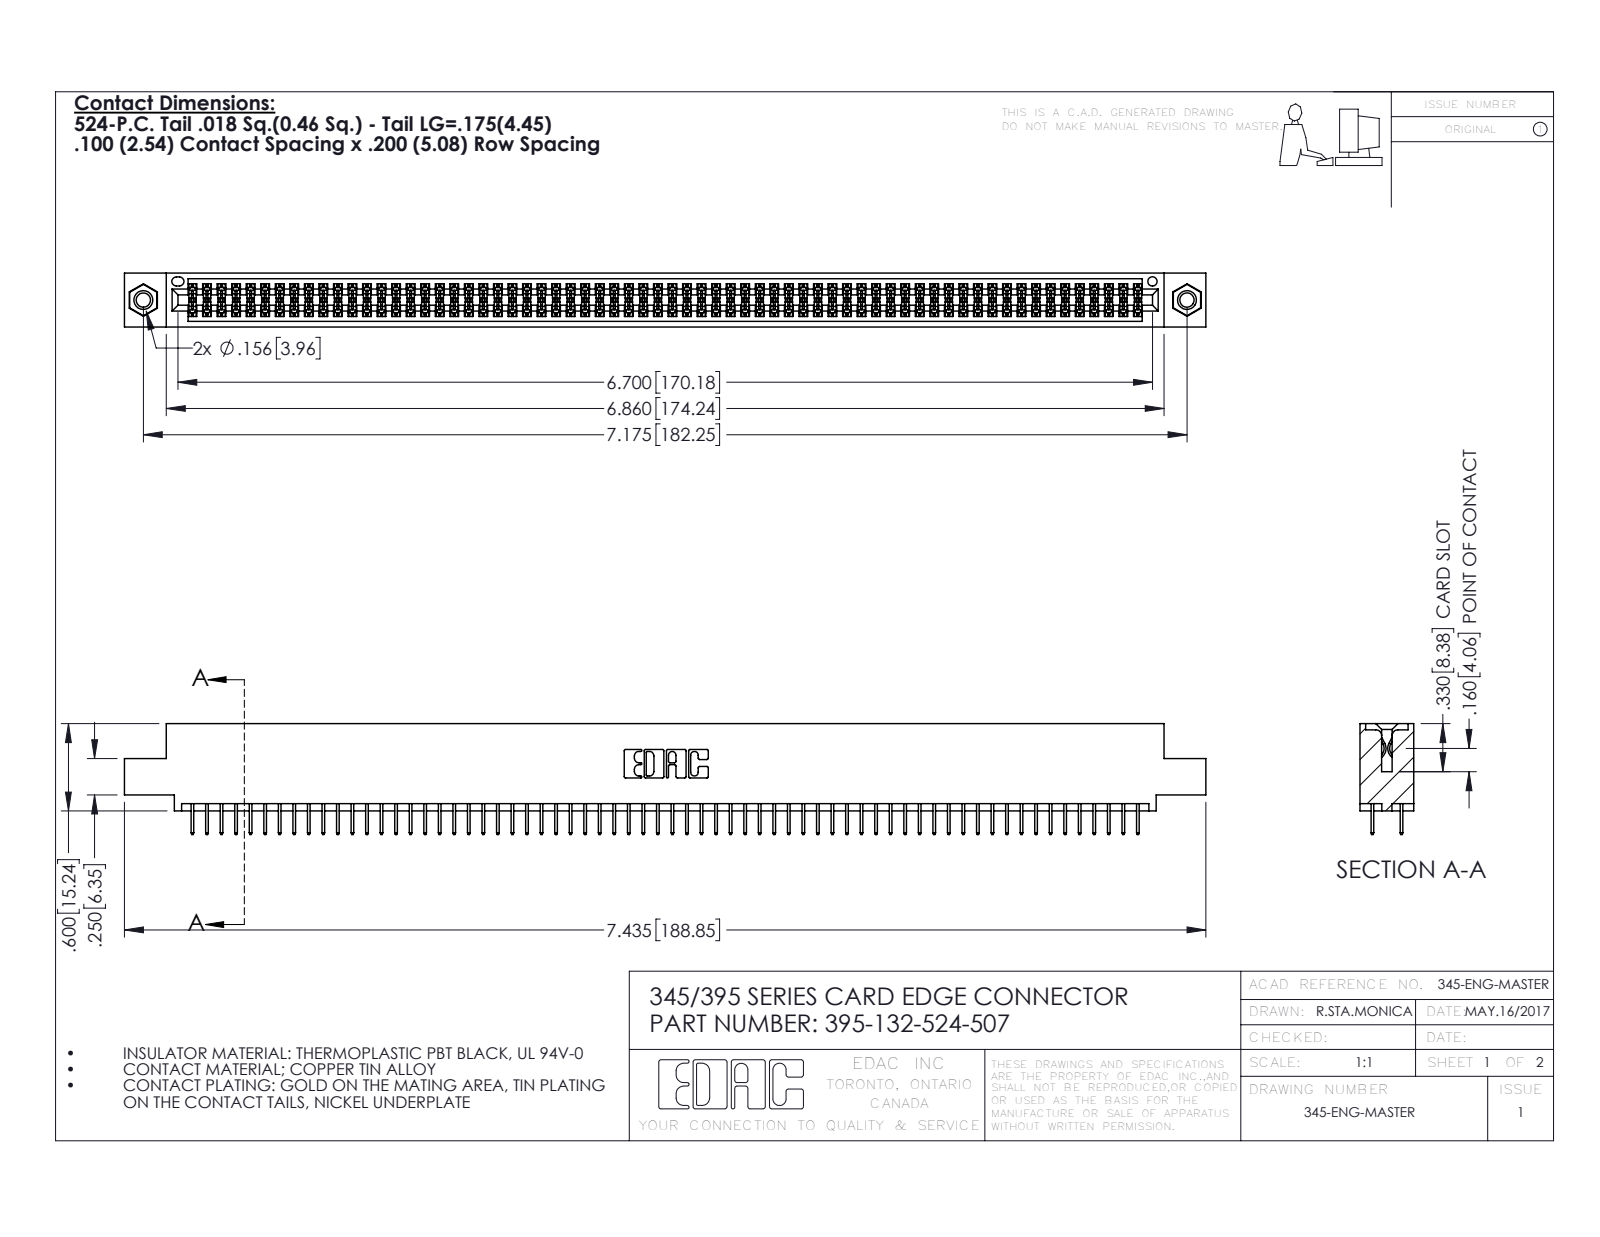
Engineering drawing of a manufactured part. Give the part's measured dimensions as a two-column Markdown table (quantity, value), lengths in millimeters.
| quantity | value |
| --- | --- |
| part name | 345-292-001_345-293-124; 345 Part_0.110 Offset - 0.156 Dia-TI; 395-132-524-507; 345-250-001_345-250-005-103 |
| STEP written by | SolidWorks 2016 (CONFIG_CONTROL_DESIGN) |
| units | millimeters |
| bodies | 135 solids, 7318 faces (5264 planar, 2038 cylindrical, 16 other) |
| overall size | 188.8 × 19.4 × 9.4 |
| volume | 18 290 mm³ |
| surface area | 27 080 mm² |
| round holes (diameter × count) | 2.5 × 2, 3.2 × 2, 4 × 2, 1.6 × 1 |
| round bosses / shafts (diameter × count) | 3.9 × 2 |
| partial cylindrical surfaces (radius × count) | 0.2 × 198, 0.3 × 22, 0.2 × 6, 0.8 × 6, 0.7 × 3, 0.4 × 2, 0.5 × 2, 0.6 × 2 |
| main face-to-face distances | 1.8, 7.6, 5.1, 9.4, 2.5, 6.9, 0.6, 5.7, 1.8, 4.4 |
| hole center spacings | 6.9, 176.3, 182.2 |
